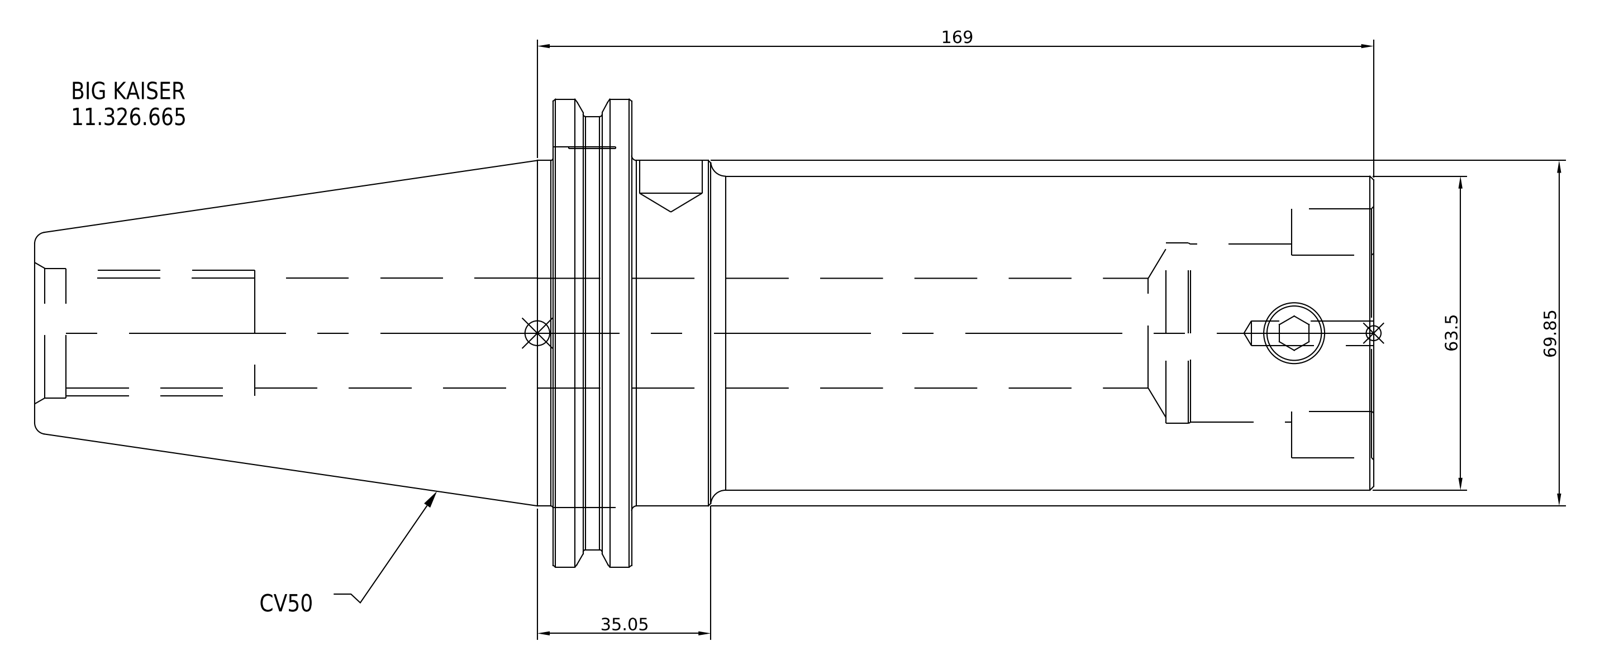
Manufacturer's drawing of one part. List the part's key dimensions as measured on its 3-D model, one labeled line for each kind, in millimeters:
Part name (STEP PRODUCT): 11.326.665
STEP written by: SolidWorks 2021 (CONFIG_CONTROL_DESIGN)
Units: millimetres
Bodies: 1 solid, 16 faces (7 planar, 6 cylindrical, 3 other)
Overall size (bounding box): 270.6 × 98.43 × 98.43
Volume: 863 780 mm³ · Surface area: 67 608 mm²
Round bosses / shafts (diameter × count): ⌀98.43 ×1, ⌀91.29 ×1, ⌀69.85 ×1, ⌀63.27 ×1
Main face-to-face distances: 17.55, 149.95, 167.5, 270.6, 120.65, 103.1, 134, 15.95, 33.5, 136.6
